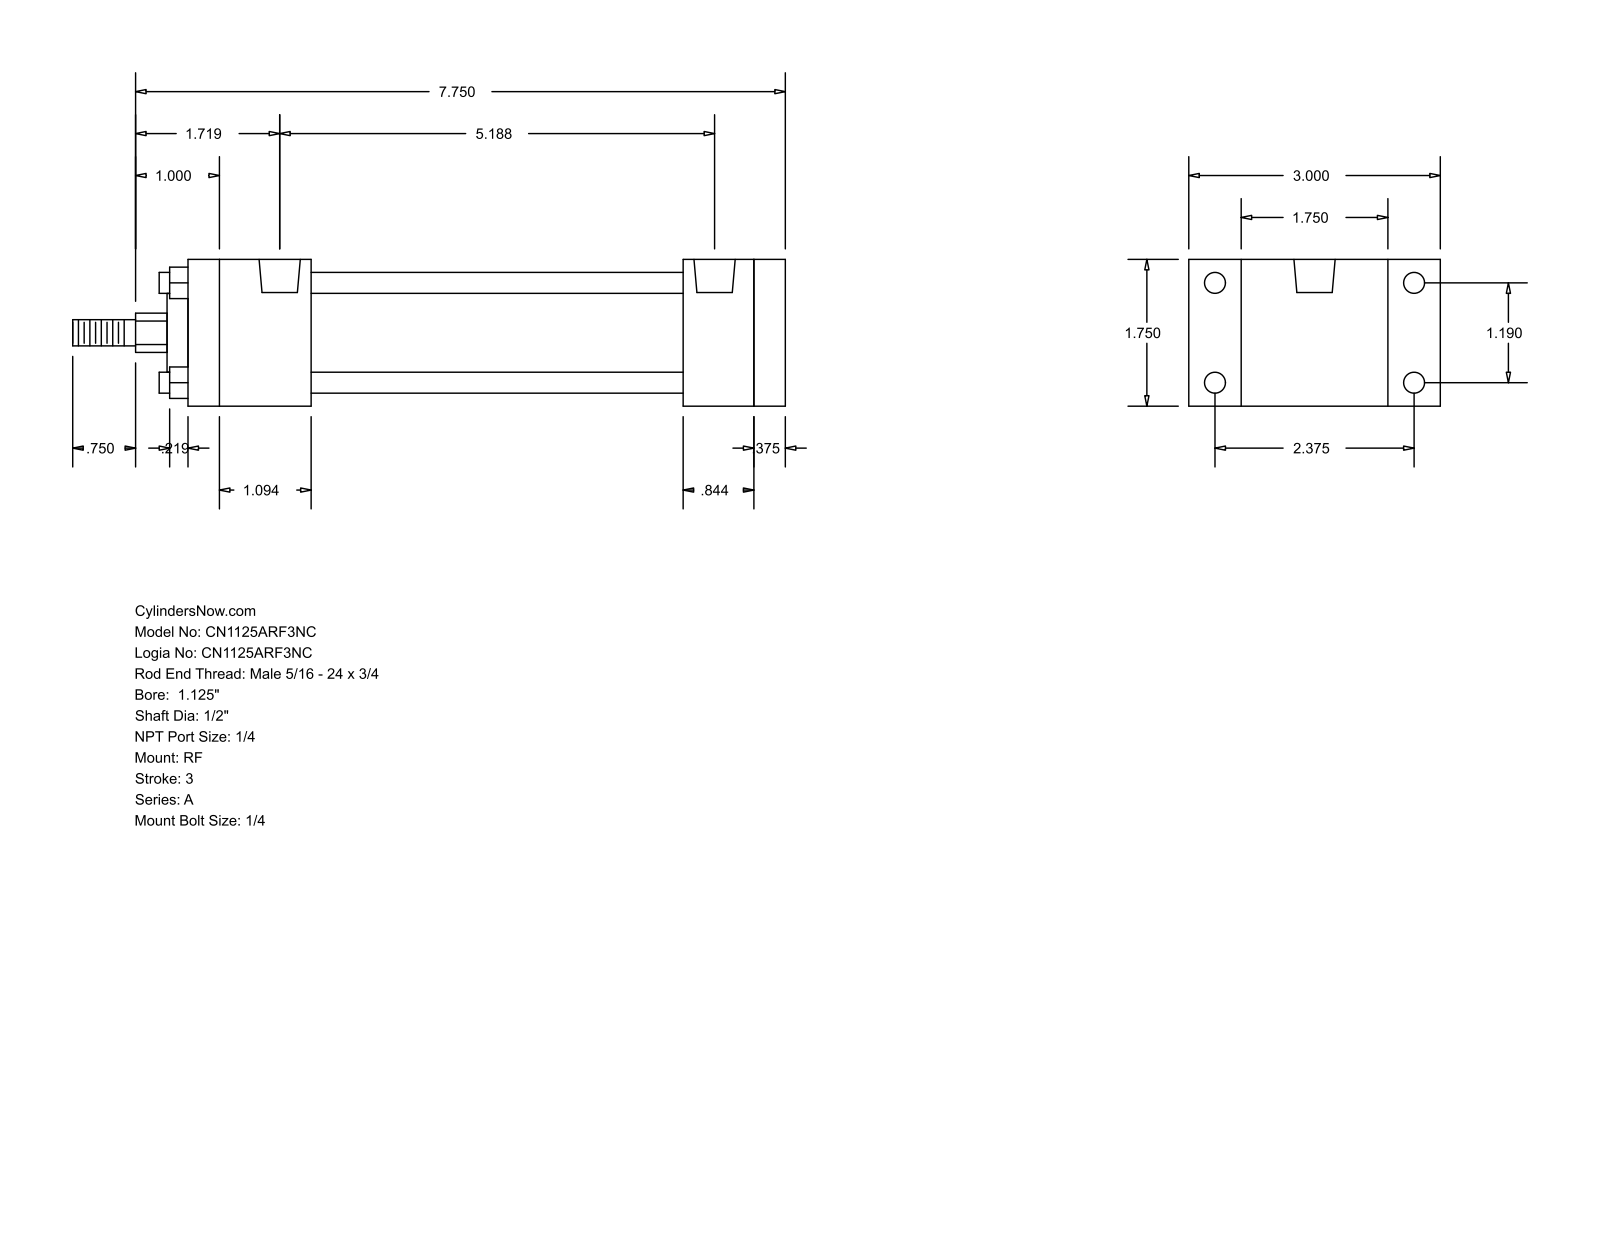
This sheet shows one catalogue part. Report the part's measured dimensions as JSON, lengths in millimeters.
{"part_name": "A_RF__0112_0.5", "step_written_by": "GSSL Pune (CONFIG_CONTROL_DESIGN)", "units": "millimeters", "bodies": {"solids": 0, "faces": 92, "planar": 64, "cylindrical": 28, "other": 0}, "overall_size": [215.9, 76.2, 44.45], "round_holes": [[5.56, 4], [6.35, 4], [12.49, 2]], "round_bosses_or_shafts": [[6.35, 4], [31.88, 1], [23.81, 1], [12.7, 1], [7.94, 1]], "partial_cylinders_radius": [[5.94, 1]], "face_to_face_distances": [44.46, 9.53, 180.97, 171.44, 37.3, 150.01, 112.71, 134.14, 143.67, 21.43], "hole_center_spacings": [30.22, 60.32, 67.47, 128.59, 1.58, 1.59, 130.17, 130.18]}
